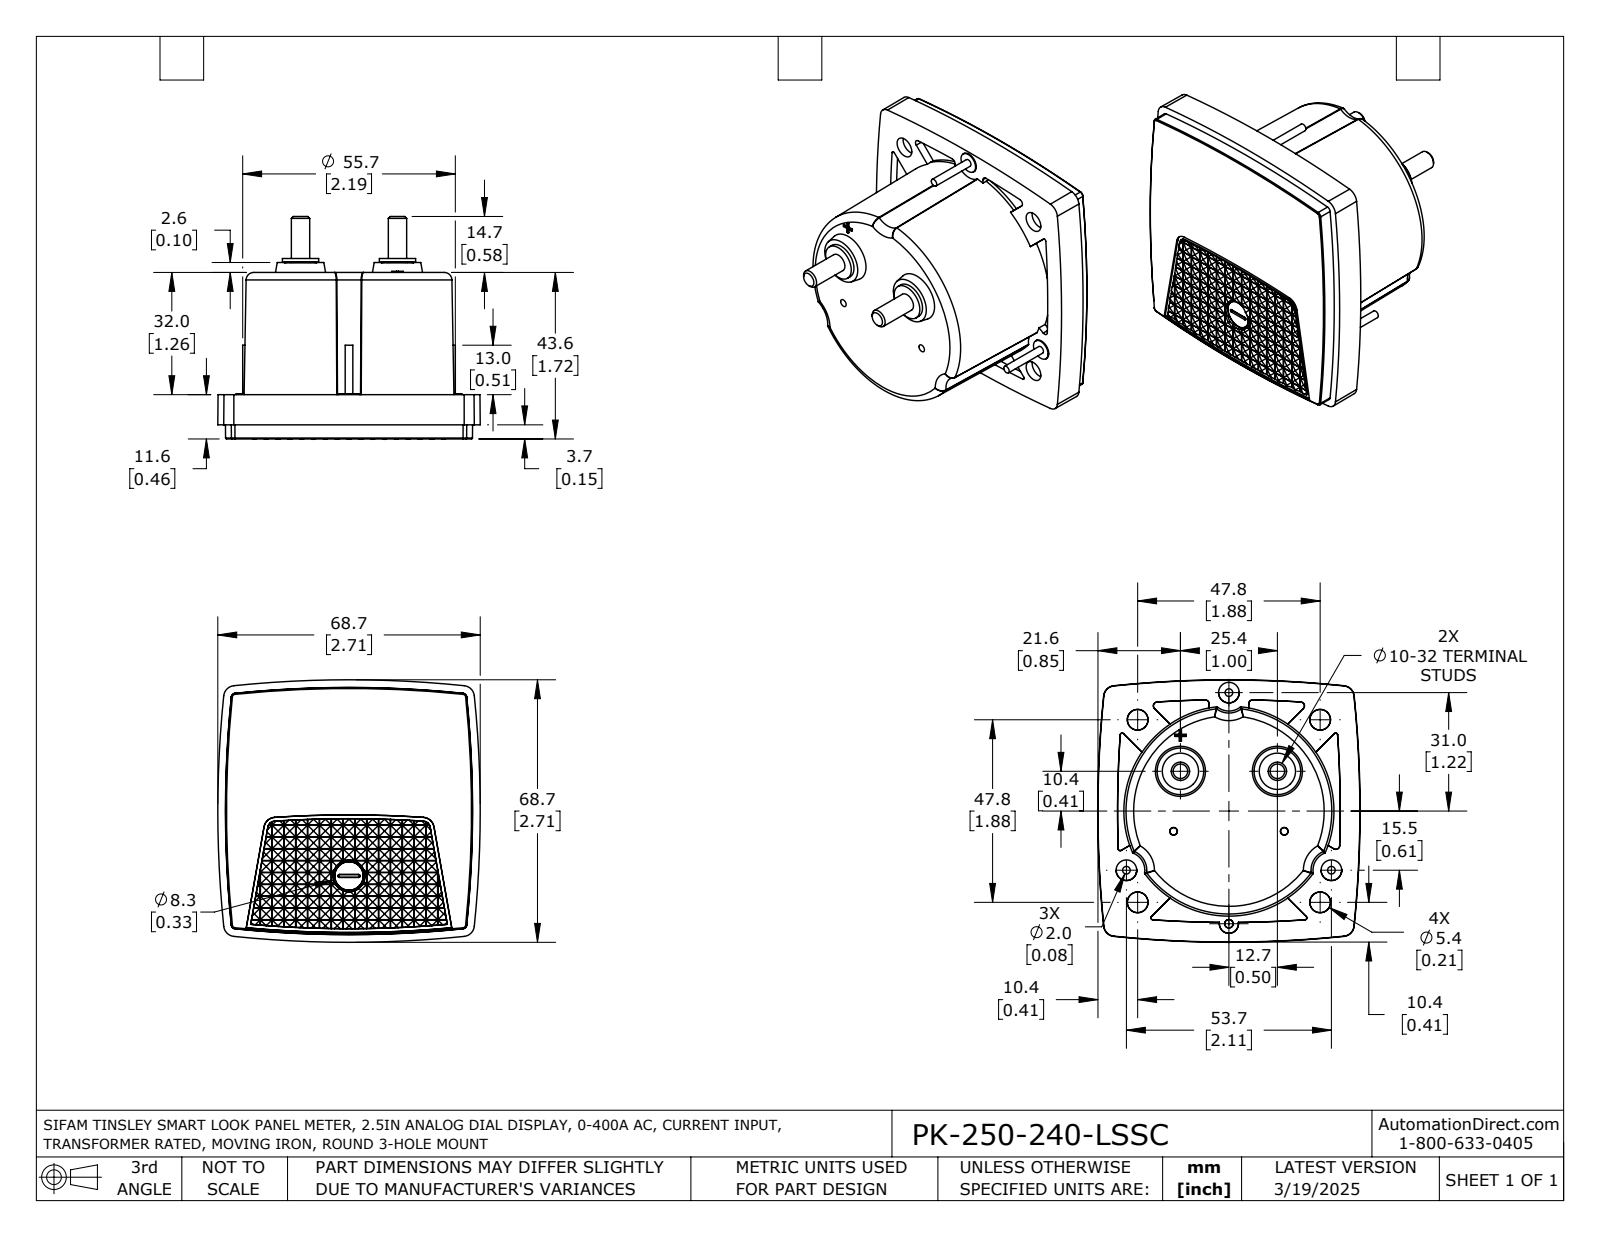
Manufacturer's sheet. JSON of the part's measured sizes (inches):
{"part_name": "PK-250-240-LSSC", "step_written_by": "SolidWorks 2021 (AUTOMOTIVE_DESIGN)", "units": "inches", "bodies": {"solids": 1, "faces": 1550, "planar": 1165, "cylindrical": 265, "other": 120}, "overall_size": [2.706, 2.706, 2.297], "volume_in3": 7.594, "surface_area_in2": 30.41, "round_bosses_or_shafts": [[0.213, 3], [0.079, 3], [0.374, 2], [0.189, 2], [0.215, 1]], "partial_cylinders_radius": [[0.167, 2], [1.083, 1]], "face_to_face_distances": [1.717, 1.26, 0.457, 0.024, 0.087, 0.096, 0.311, 0.12, 0.072, 1.346]}
